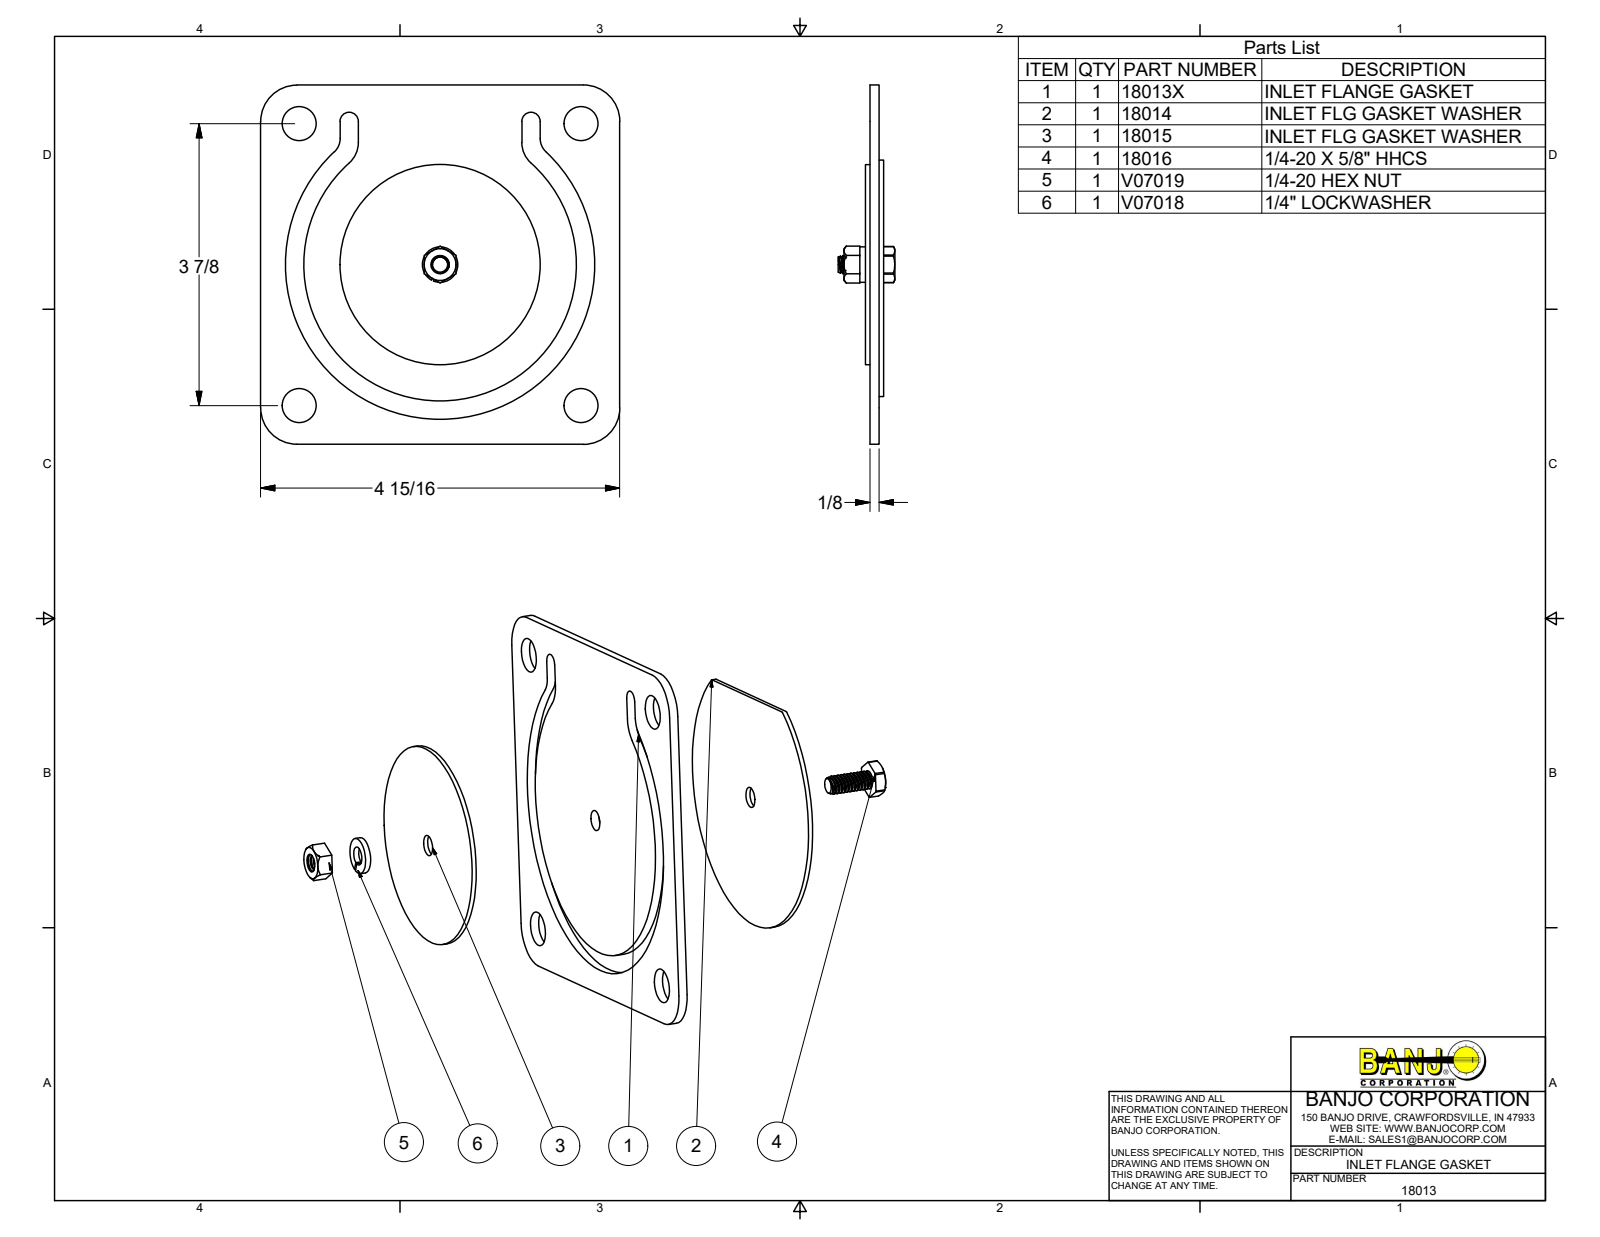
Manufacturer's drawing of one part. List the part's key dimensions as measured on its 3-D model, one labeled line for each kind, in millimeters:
Part name (STEP PRODUCT): 18013X; 18014; 18015; 18016 (+3 more)
STEP written by: Autodesk Inventor 2014 (AUTOMOTIVE_DESIGN)
Units: millimetres
Bodies: 6 solids, 222 faces (36 planar, 101 cylindrical, 85 other)
Overall size (bounding box): 125.41 × 125.41 × 19.84
Volume: 59 813 mm³ · Surface area: 53 108 mm²
Round holes (diameter × count): ⌀11.91 ×4, ⌀4.98 ×1, ⌀6.4 ×1, ⌀7.14 ×1
Round bosses / shafts (diameter × count): ⌀5.39 ×12, ⌀69.85 ×1, ⌀12.42 ×1, ⌀6.35 ×1
Partial cylindrical surfaces — rounded edges, fillets, slot ends (radius × count): R12.7 ×4, R0.76 ×2, R3.17 ×2, R6.35 ×2, R9.53 ×2, R2.69 ×1, R6.29 ×1, R46.04 ×1
Main face-to-face distances: 3.17, 1.59, 4.76, 6.35, 125.42, 11.12, 1.95, 3.54, 6.71, 8.3
Hole centre spacings: 69.59, 98.42, 139.19
